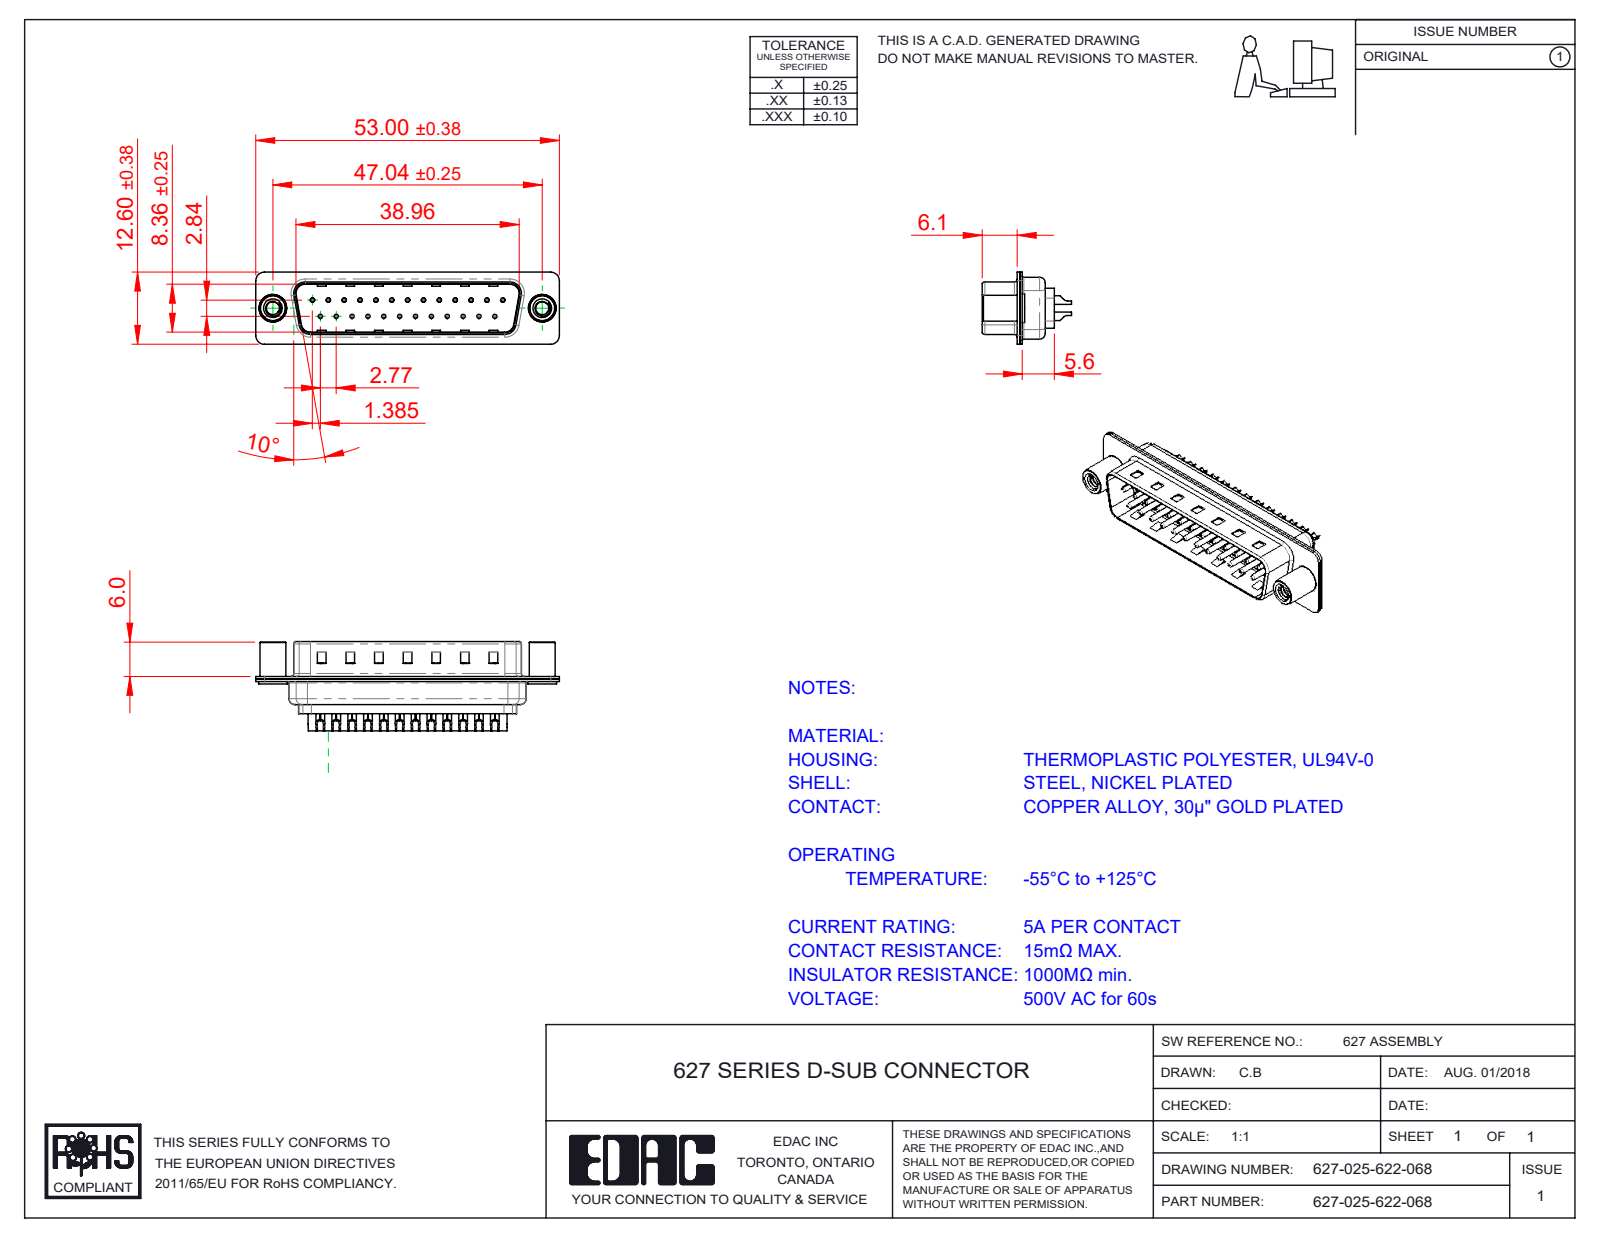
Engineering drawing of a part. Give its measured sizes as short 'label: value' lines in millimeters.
name: 627-025-622-068; 627 Contact Row 2_22L; 627 Housing_25 LP; 627 Shell Front_25 Contacts (+3 more)
written by: SolidWorks 2020 (CONFIG_CONTROL_DESIGN)
unit: mm
bodies: 30 solids, 2010 faces (523 planar, 890 cylindrical, 597 other)
size: 53 × 15.35 × 12.6
volume: 2 754 mm³; area: 8 051 mm²
holes: 25× ⌀0.35, 25× ⌀1.1, 25× ⌀1.6, 2× ⌀2.26, 2× ⌀4, 2× ⌀4.8
bosses: 25× ⌀2, 25× ⌀1.5, 25× ⌀0.75, 2× ⌀5, 2× ⌀4.9, 2× ⌀4.5
rounds: 16× R1.5, 12× R2, 8× R0.5, 8× R1.6, 6× R1, 4× R0.25, 4× R0.6, 4× R0.65
face distances: 0.4, 0.45, 0.82, 9.58, 0.9, 8.76, 1.5, 1.4, 6.5, 6.05
hole spacings: 3.16, 8.31, 2.77, 5.54, 11.08, 16.62, 5.03, 5.04
